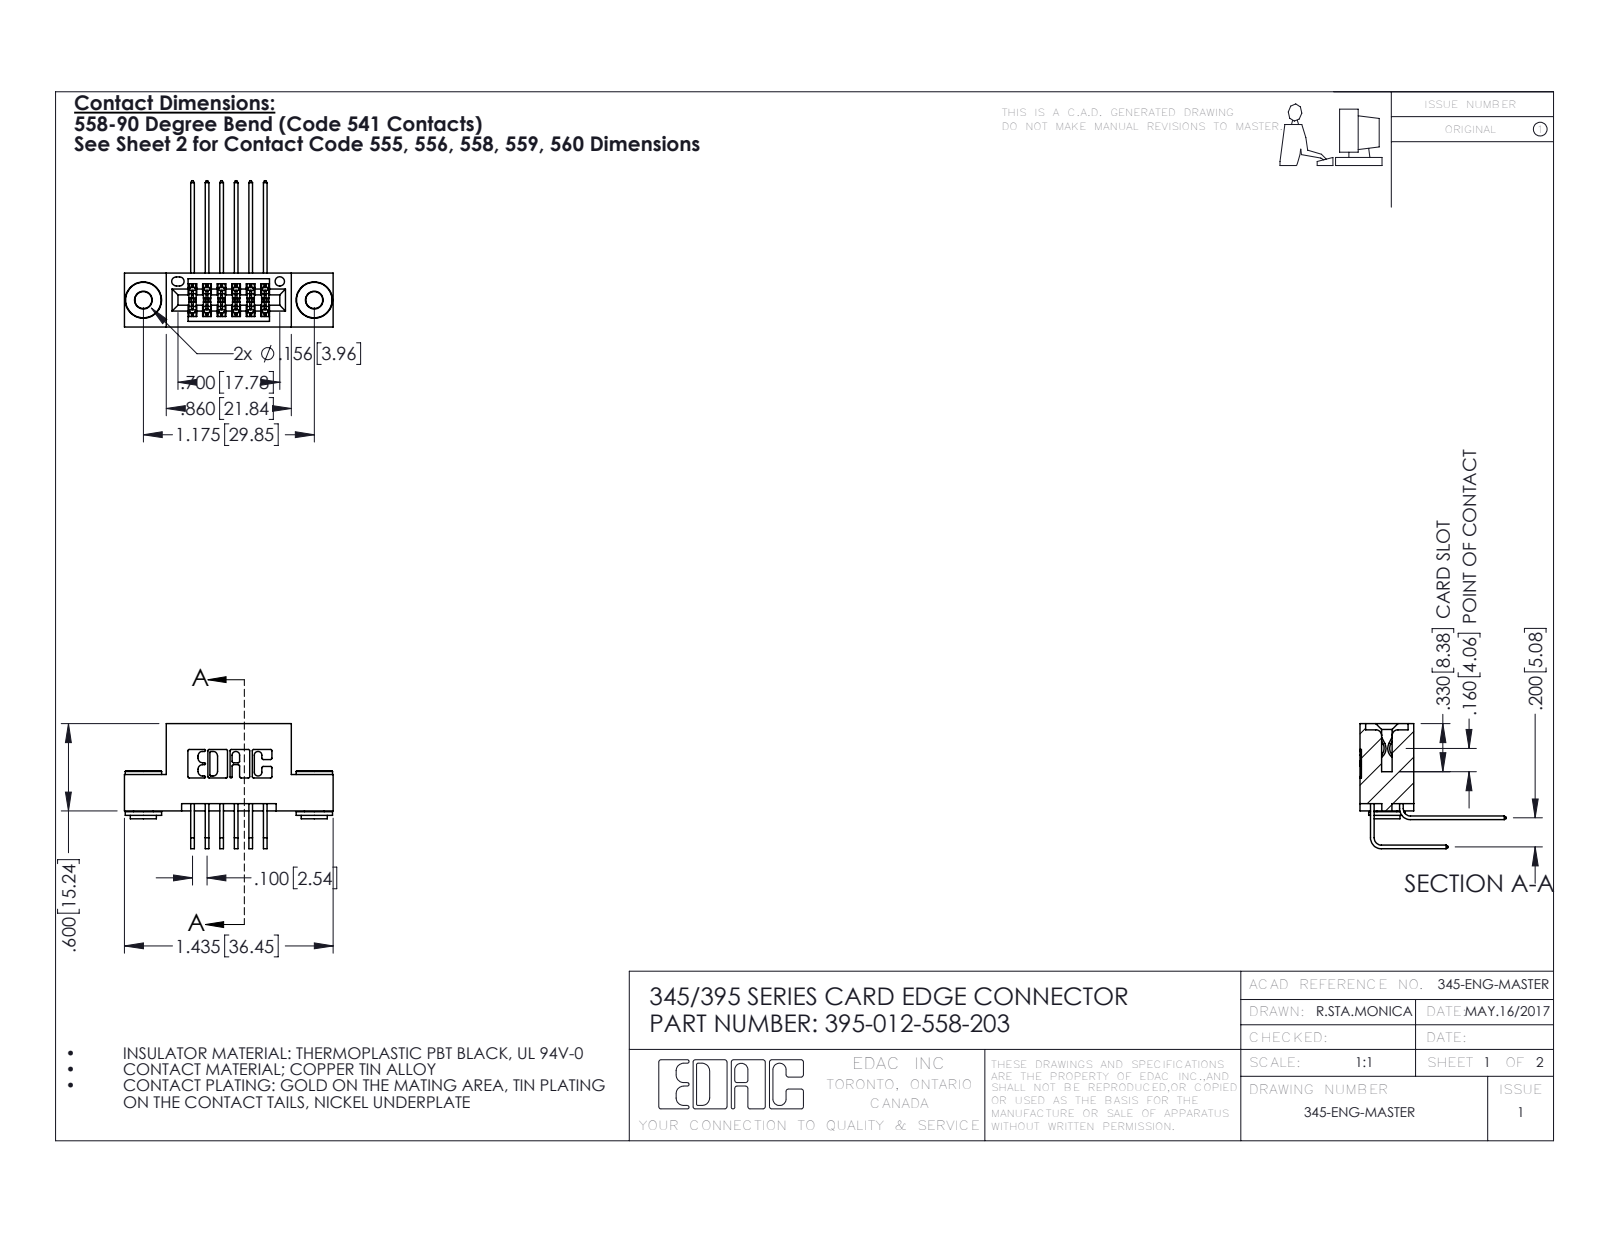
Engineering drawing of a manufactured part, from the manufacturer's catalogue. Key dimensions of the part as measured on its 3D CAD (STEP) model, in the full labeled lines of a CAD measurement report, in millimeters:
Part name (STEP PRODUCT): 345 Part_Flush Mounting Lugs - 0.156 Dia-TH; 395-012-558-203; 345-292-001_558 Tail - 2; 345-250-002_345-250-002-102 (+1 more)
STEP written by: SolidWorks 2016 (CONFIG_CONTROL_DESIGN)
Units: millimetres
Bodies: 15 solids, 788 faces (510 planar, 270 cylindrical, 8 other)
Overall size (bounding box): 36.4 × 25.5 × 21.8
Volume: 3 290 mm³ · Surface area: 4 704 mm²
Round holes (diameter × count): ⌀2.9 ×2, ⌀4 ×2, ⌀1.6 ×1
Round bosses / shafts (diameter × count): ⌀6.4 ×2, ⌀4.6 ×2, ⌀3.5 ×2
Partial cylindrical surfaces — rounded edges, fillets, slot ends (radius × count): R0.3 ×22, R0.2 ×19, R0.2 ×6, R0.8 ×6, R0.7 ×3, R0.4 ×2, R0.5 ×2, R0.6 ×2
Main face-to-face distances: 5.1, 2.5, 1.8, 7.6, 9.4, 0.6, 7.6, 2.5, 6.9, 5.7
Hole centre spacings: 6.9, 24, 29.8
